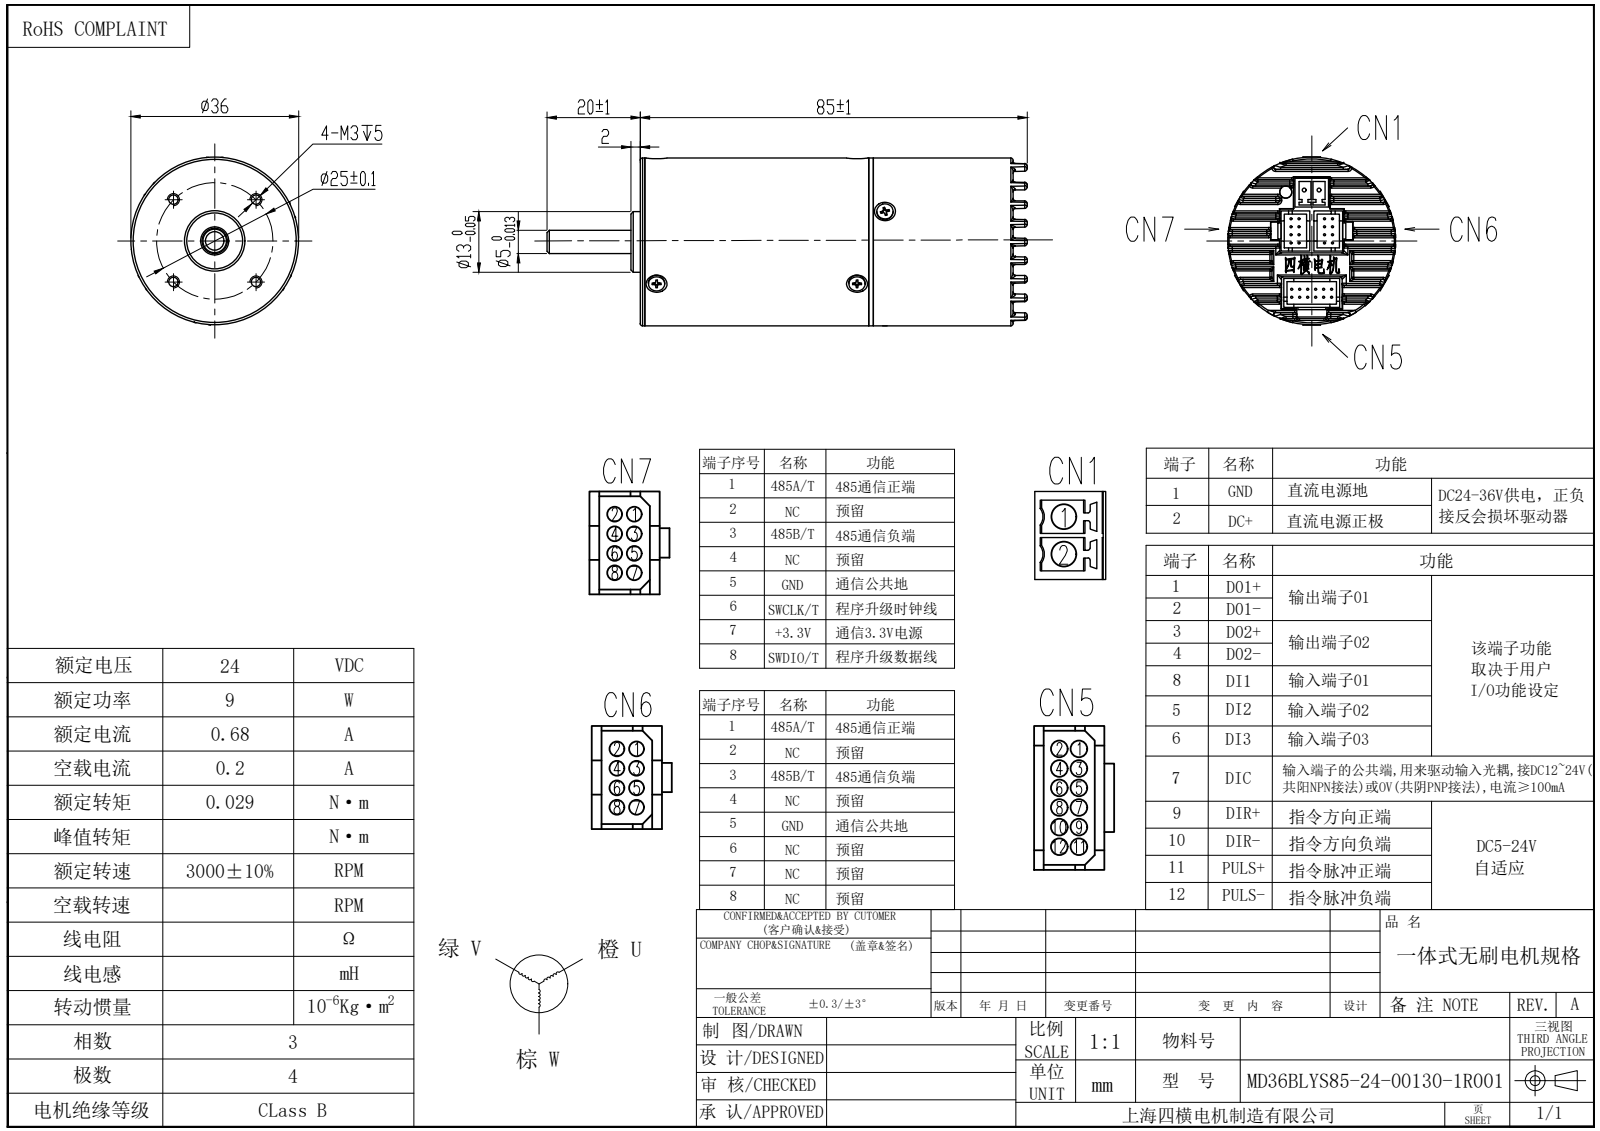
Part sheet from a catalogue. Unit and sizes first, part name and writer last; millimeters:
Units: millimetres
Overall size (bounding box): 98 × 36.01 × 36
Round holes (diameter × count): ⌀1.6 ×9, ⌀2.4 ×6, ⌀2.05 ×5, ⌀4 ×1, ⌀5 ×1, ⌀6 ×1, ⌀20 ×1, ⌀25 ×1, ⌀34 ×1
Round bosses / shafts (diameter × count): ⌀3.5 ×9, ⌀2 ×9, ⌀36 ×1, ⌀32 ×1, ⌀13 ×1
Partial cylindrical surfaces — rounded edges, fillets, slot ends (radius × count): R0.3 ×36, R0.5 ×36
Main face-to-face distances: 6, 16, 10, 48, 49, 1, 12, 4, 65, 55
Hole centre spacings: 43, 6.5, 12.5, 12.51, 17.68, 25, 17.67, 17.69
Volume: 36 936 mm³ · Surface area: 28 404 mm²
Bodies: 15 solids, 1582 faces (193 planar, 490 cylindrical, 899 other)
Part name (STEP PRODUCT): 36BLY轴; 36BLY装配体; 36BLYS后端盖; 后罩 (+3 more)
STEP written by: SolidWorks 2020 (AUTOMOTIVE_DESIGN)
